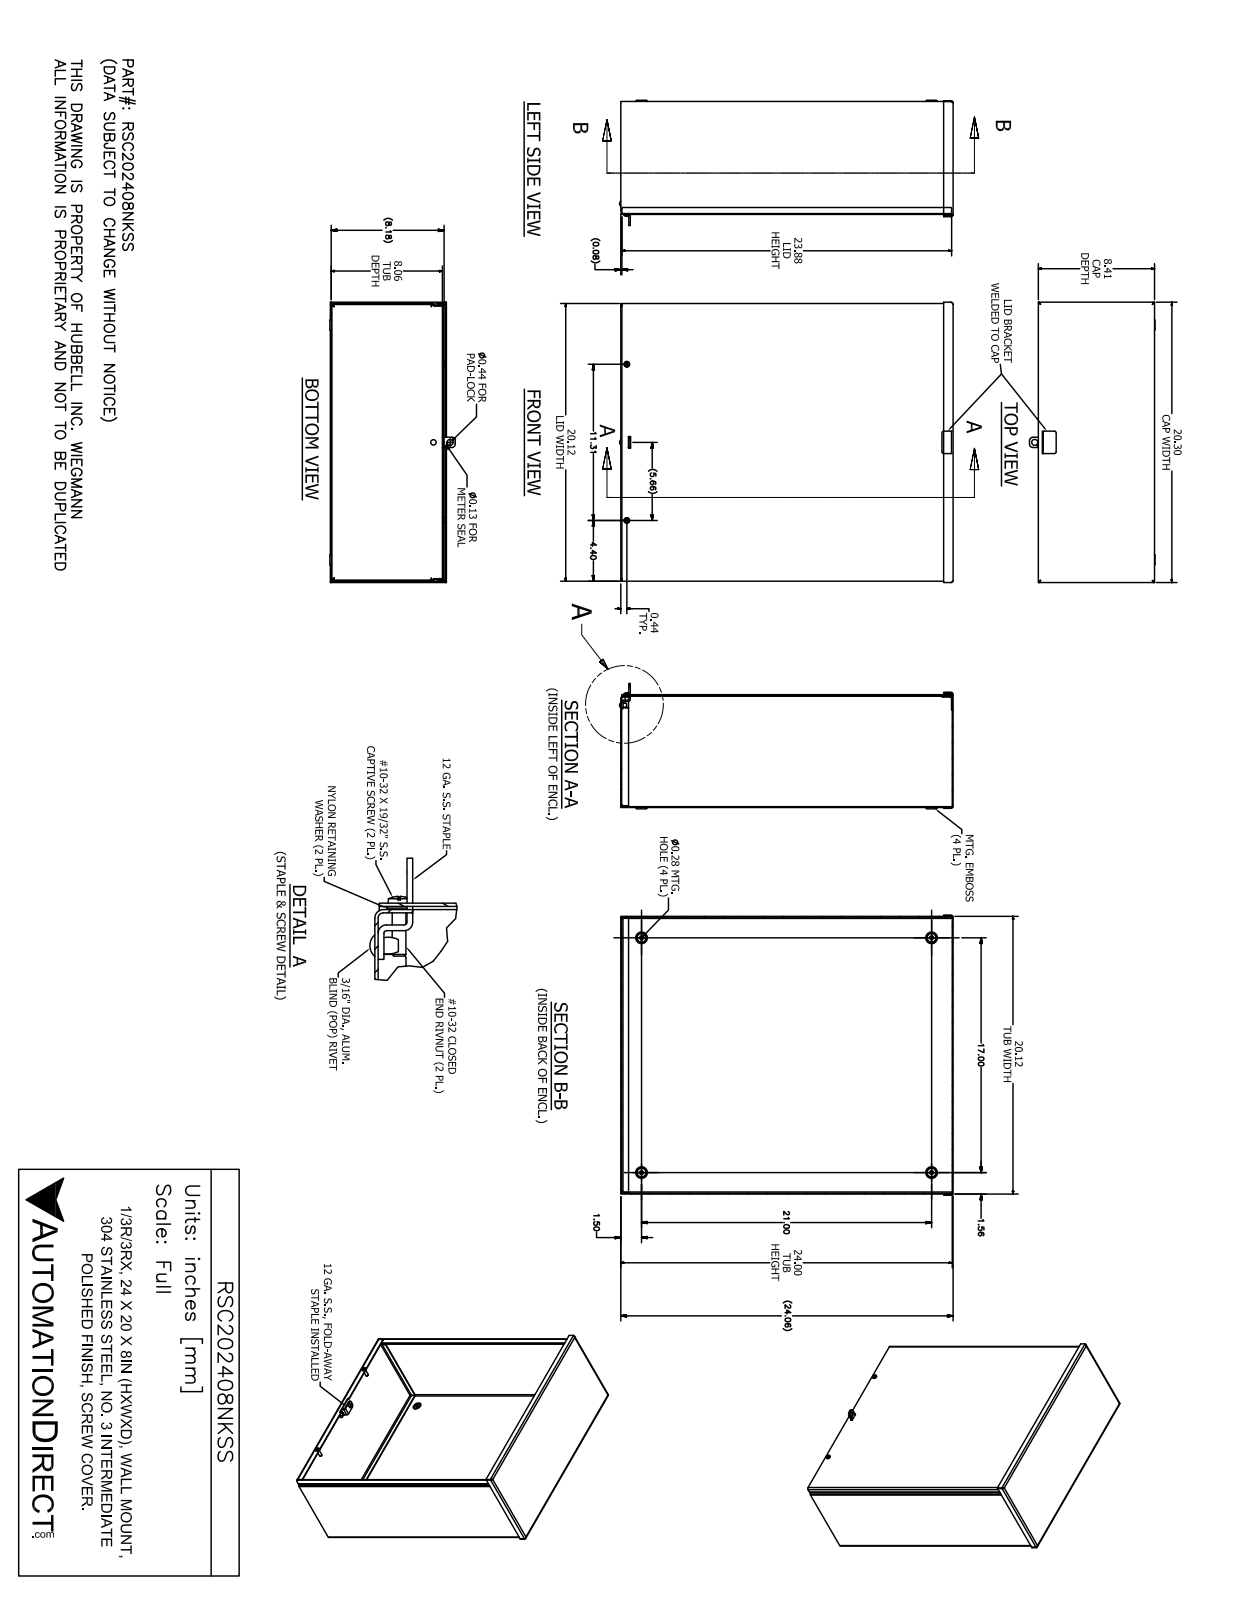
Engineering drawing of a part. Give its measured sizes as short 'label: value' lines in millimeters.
name: RSC202408NKSS
written by: SolidWorks 2017 (AUTOMOTIVE_DESIGN)
unit: mm
bodies: 13 solids, 383 faces (199 planar, 99 cylindrical, 85 other)
size: 613.4 × 515.6 × 230.7
volume: 1 703 000 mm³; area: 2 285 000 mm²
holes: 4× ⌀6.4, 4× ⌀7.1, 2× ⌀4, 2× ⌀5, 2× ⌀6.5, 2× ⌀7.1, 1× ⌀3.2, 1× ⌀5, 1× ⌀5.1, 1× ⌀11.1
bosses: 2× ⌀11.5, 2× ⌀10.3, 2× ⌀6.3, 2× ⌀4.2, 1× ⌀4.7
rounds: 17× R2.4, 17× R3.9, 6× R0.8, 4× R3.2, 4× R6.4, 3× R1.6, 2× R1.2, 2× R1.3
face distances: 1.5, 206.2, 207.7, 204.7, 509.5, 609.6, 508, 511, 611.1, 608.1
hole spacings: 77.1, 77.4, 287.4, 360.6, 360.6, 431.8, 533.4, 565
